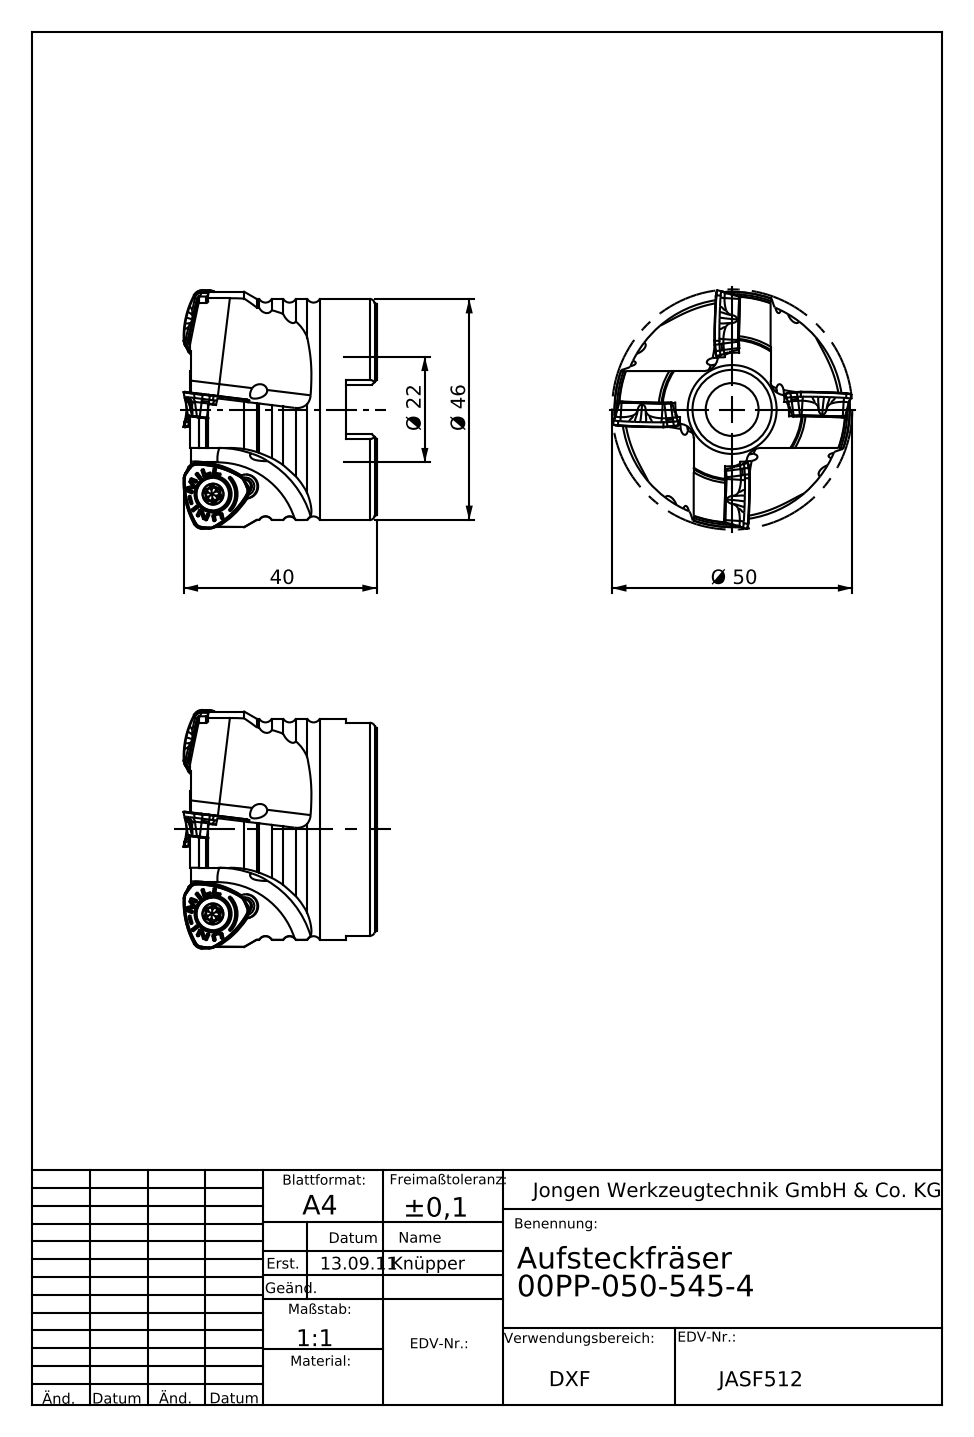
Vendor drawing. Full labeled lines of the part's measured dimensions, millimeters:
Part name (STEP PRODUCT): 00PP-050-545-4
STEP written by: SolidWorks 2010 (AUTOMOTIVE_DESIGN)
Units: millimetres
Bodies: 1 solid, 91 faces (19 planar, 22 cylindrical, 50 other)
Overall size (bounding box): 50 × 50 × 40.24
Volume: 55 228 mm³ · Surface area: 11 553 mm²
Round holes (diameter × count): ⌀11 ×1, ⌀11.69 ×1, ⌀16.5 ×1, ⌀22 ×1, ⌀22.15 ×1, ⌀22.3 ×1
Round bosses / shafts (diameter × count): ⌀49 ×1, ⌀46 ×1
Main face-to-face distances: 38.95, 6.3, 32.65, 10.4, 27.95, 21.65, 11, 20, 13.7, 7.95
